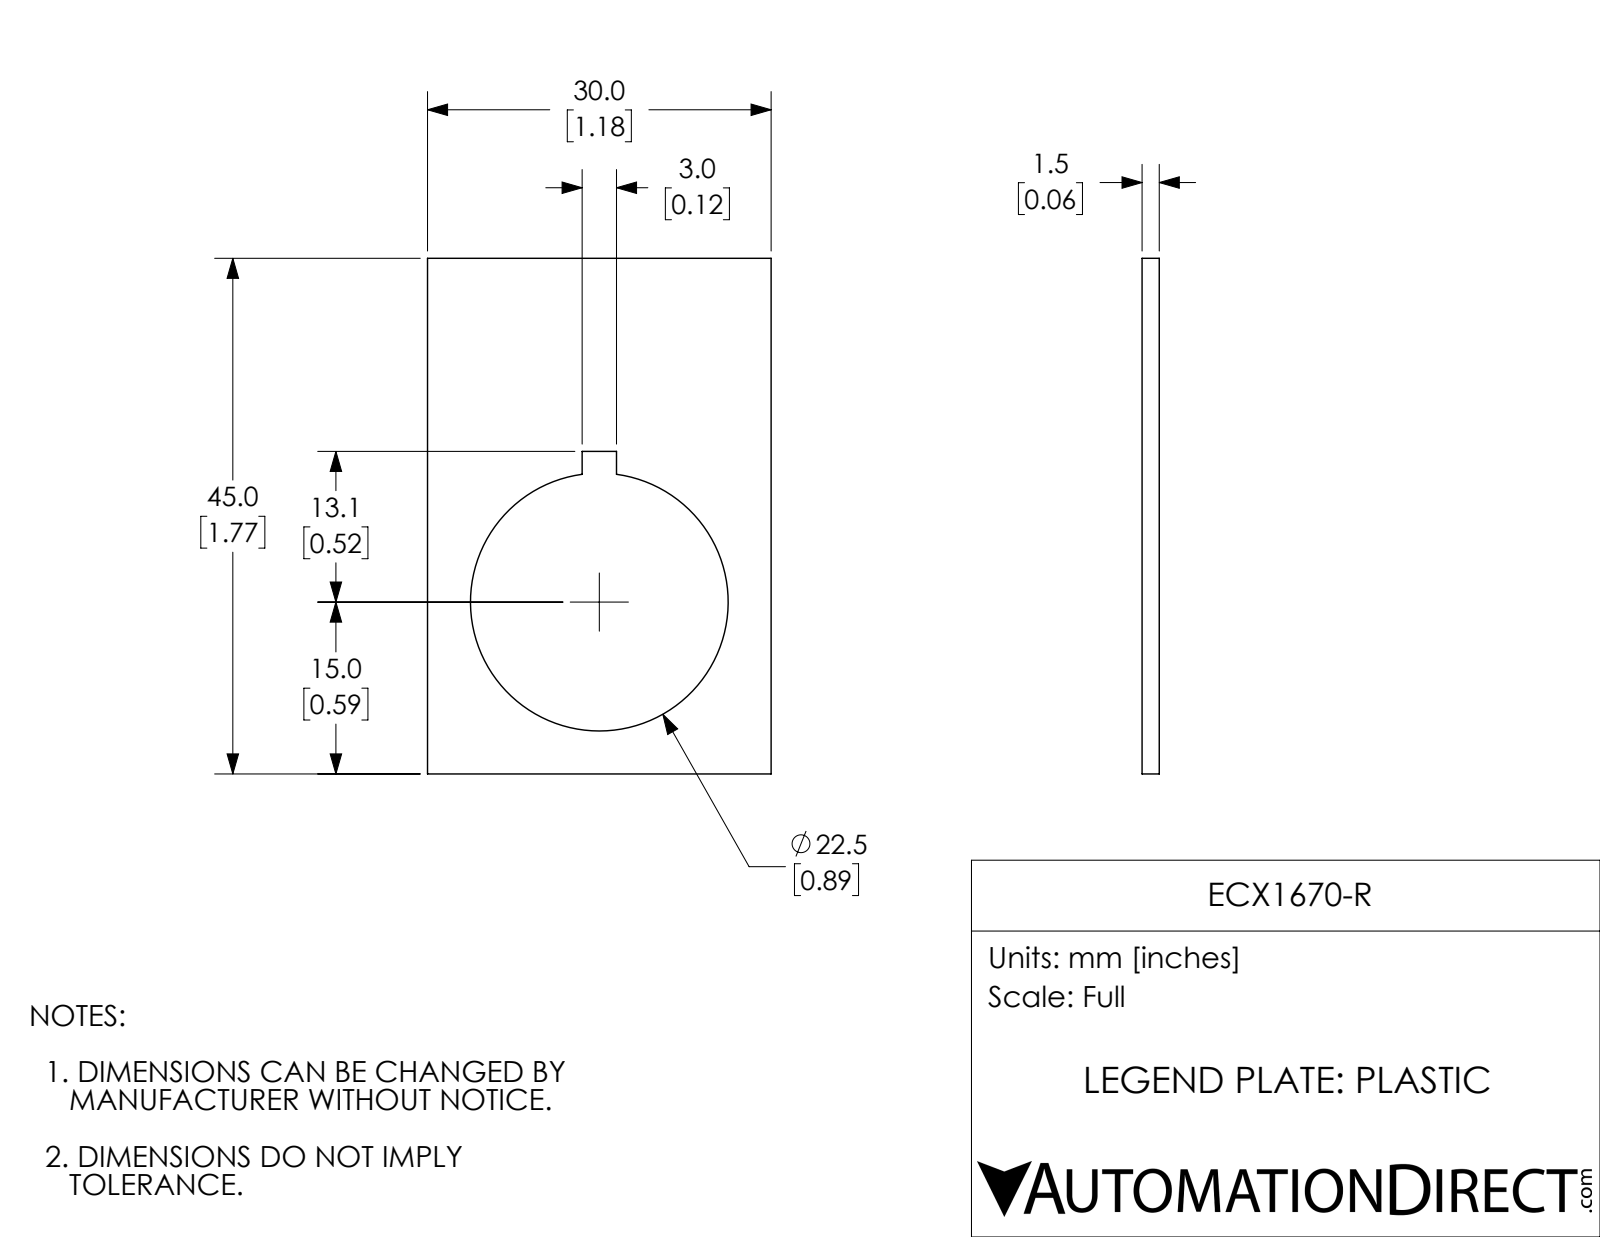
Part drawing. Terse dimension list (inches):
name: ECX1670-R
written by: SolidWorks 2017 (AUTOMOTIVE_DESIGN)
unit: in
bodies: 1 solid, 12 faces (9 planar, 3 cylindrical, 0 other)
size: 1.772 × 1.181 × 0.059
volume: 0.087 in³; area: 3.457 in²
holes: 1× ⌀0.886
face distances: 0.059, 1.181, 1.772, 0.531, 0.65, 1.108, 0.663, 0.118
